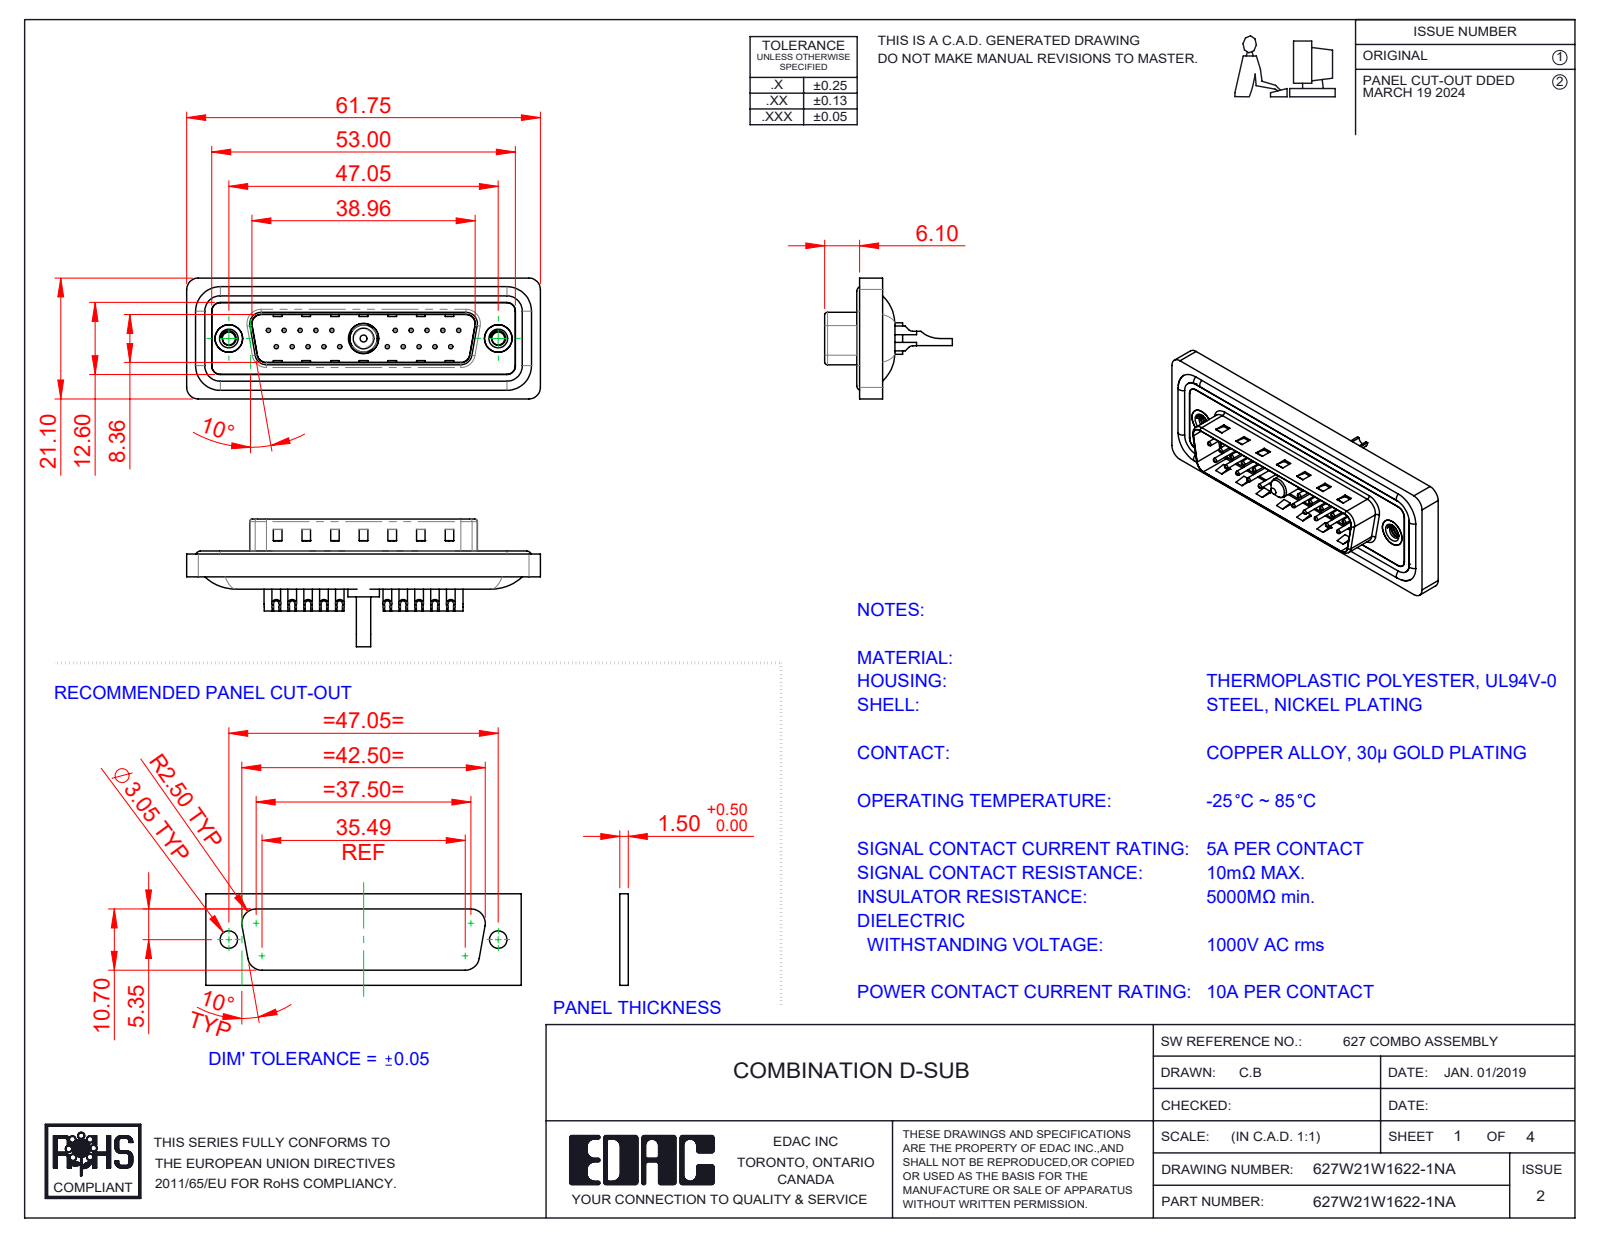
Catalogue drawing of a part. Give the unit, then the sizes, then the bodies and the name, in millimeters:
Units: millimetres
Overall size (bounding box): 61.75 × 22.3 × 21.1
Round holes (diameter × count): ⌀0.75 ×20, ⌀1 ×20, ⌀1.6 ×20, ⌀2 ×20, ⌀2.26 ×2, ⌀4 ×2, ⌀4.8 ×2, ⌀5 ×2, ⌀1.7 ×1, ⌀4.85 ×1, ⌀5.3 ×1
Round bosses / shafts (diameter × count): ⌀1.5 ×20, ⌀1.6 ×4, ⌀4.9 ×2, ⌀5.5 ×1, ⌀5.2 ×1, ⌀4.75 ×1, ⌀3.75 ×1, ⌀3.6 ×1
Partial cylindrical surfaces — rounded edges, fillets, slot ends (radius × count): R1.5 ×22, R2 ×18, R0.5 ×8, R1.6 ×8, R1 ×6, R0.25 ×4, R0.6 ×4, R0.65 ×4
Main face-to-face distances: 0.4, 1.5, 1.1, 1.6, 0.5, 3.1, 2.9, 4.1, 0.82, 9.58
Hole centre spacings: 3.16, 2.77, 5.54, 8.31, 5.04, 19.39, 20.97, 22.16
Volume: 7 227 mm³ · Surface area: 12 158 mm²
Bodies: 29 solids, 1266 faces (401 planar, 532 cylindrical, 333 other)
Part name (STEP PRODUCT): 627Combo Contact Row 2_22; 627Combo Shell Front_25 Contacts; 627Combo Waterproof Housing_25 Contacts; 627Combo Threaded Rivet_A (+5 more)
STEP written by: SolidWorks 2023 (CONFIG_CONTROL_DESIGN)
